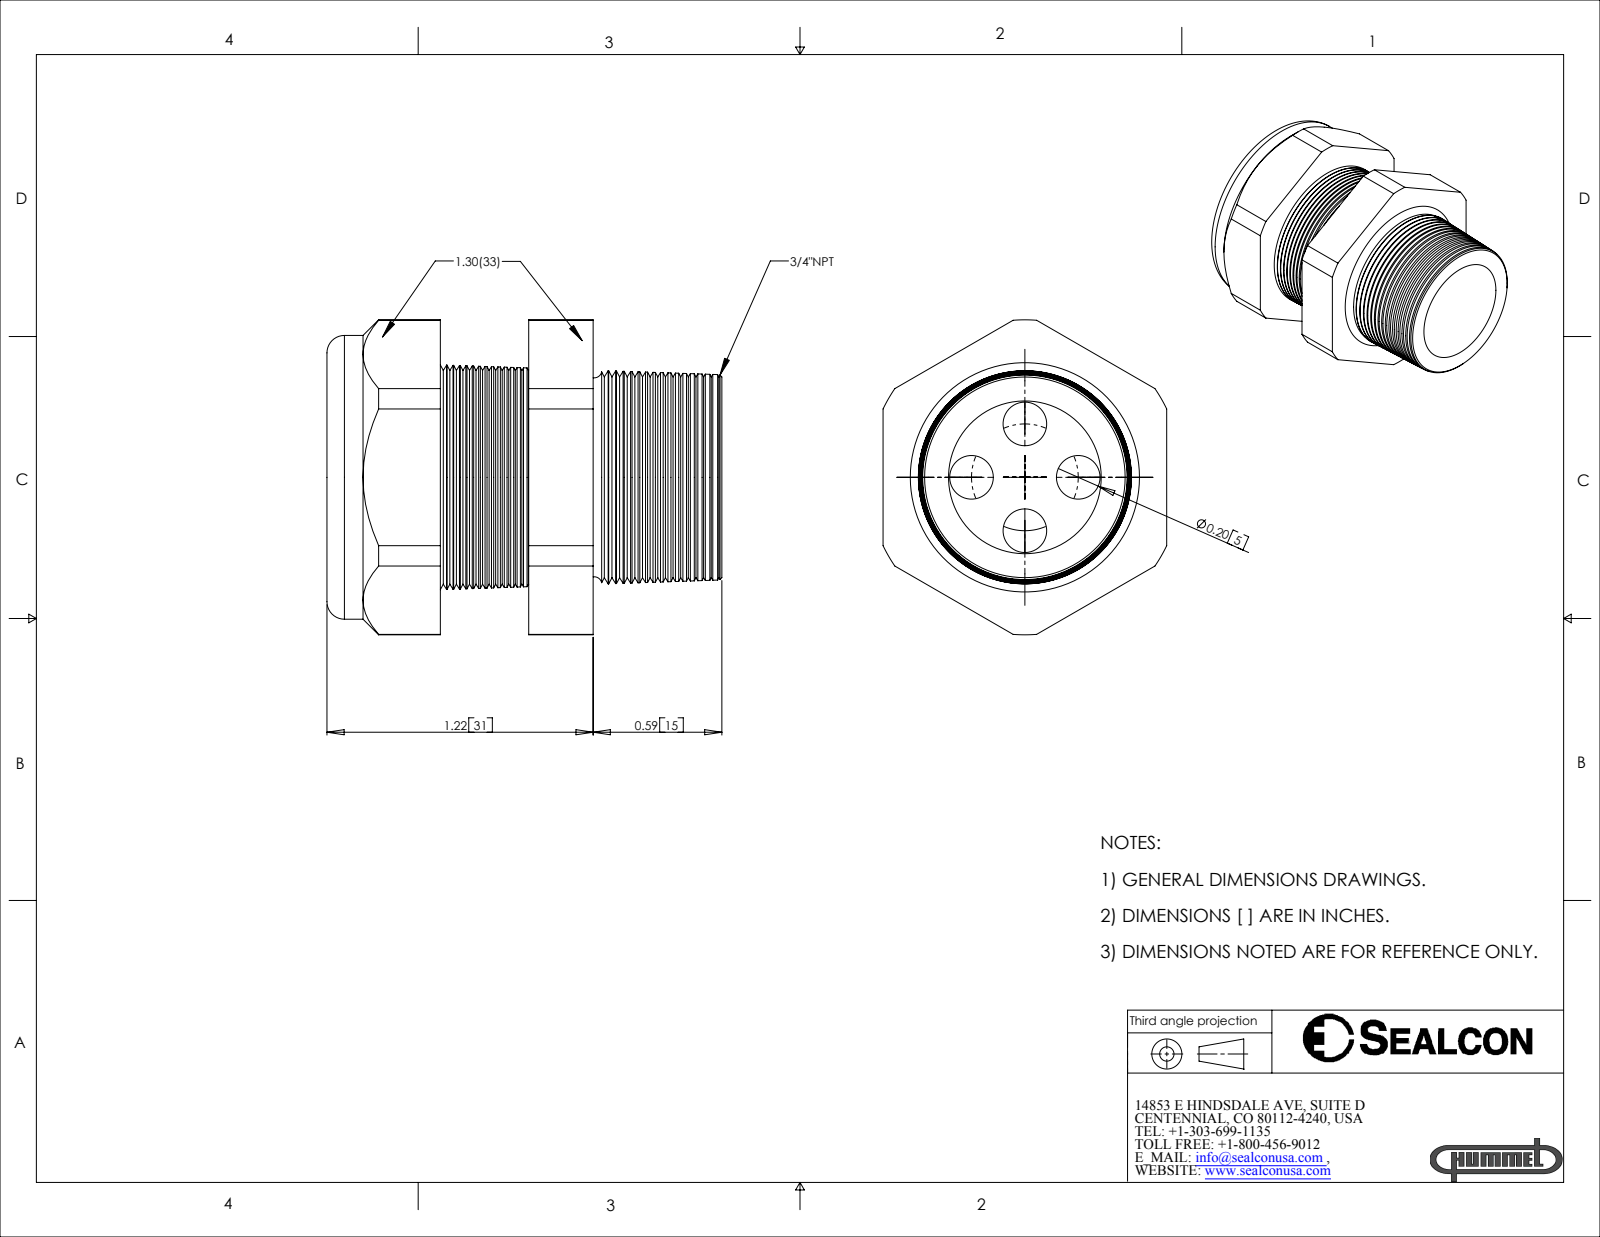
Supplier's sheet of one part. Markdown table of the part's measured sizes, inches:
| quantity | value |
| --- | --- |
| part name | CD21N6-BK |
| STEP written by | SolidWorks 2007 (CONFIG_CONTROL_DESIGN) |
| units | inches |
| bodies | 2 solids, 242 faces (20 planar, 28 cylindrical, 194 other) |
| overall size | 1.81 × 1.443 × 1.3 |
| volume | 1.262 in³ |
| surface area | 18.16 in² |
| round holes (diameter × count) | 0.2 × 4, 0.69 × 1, 0.71 × 1 |
| round bosses / shafts (diameter × count) | 1.3 × 1 |
| partial cylindrical surfaces (radius × count) | 0.721 × 1 |
| main face-to-face distances | 1.3, 0.925, 0.52, 0.405, 1.22, 0.7, 0.295, 1.81, 1.29, 0.885 |
| hole center spacings | 0.244, 0.346, 0.489 |
